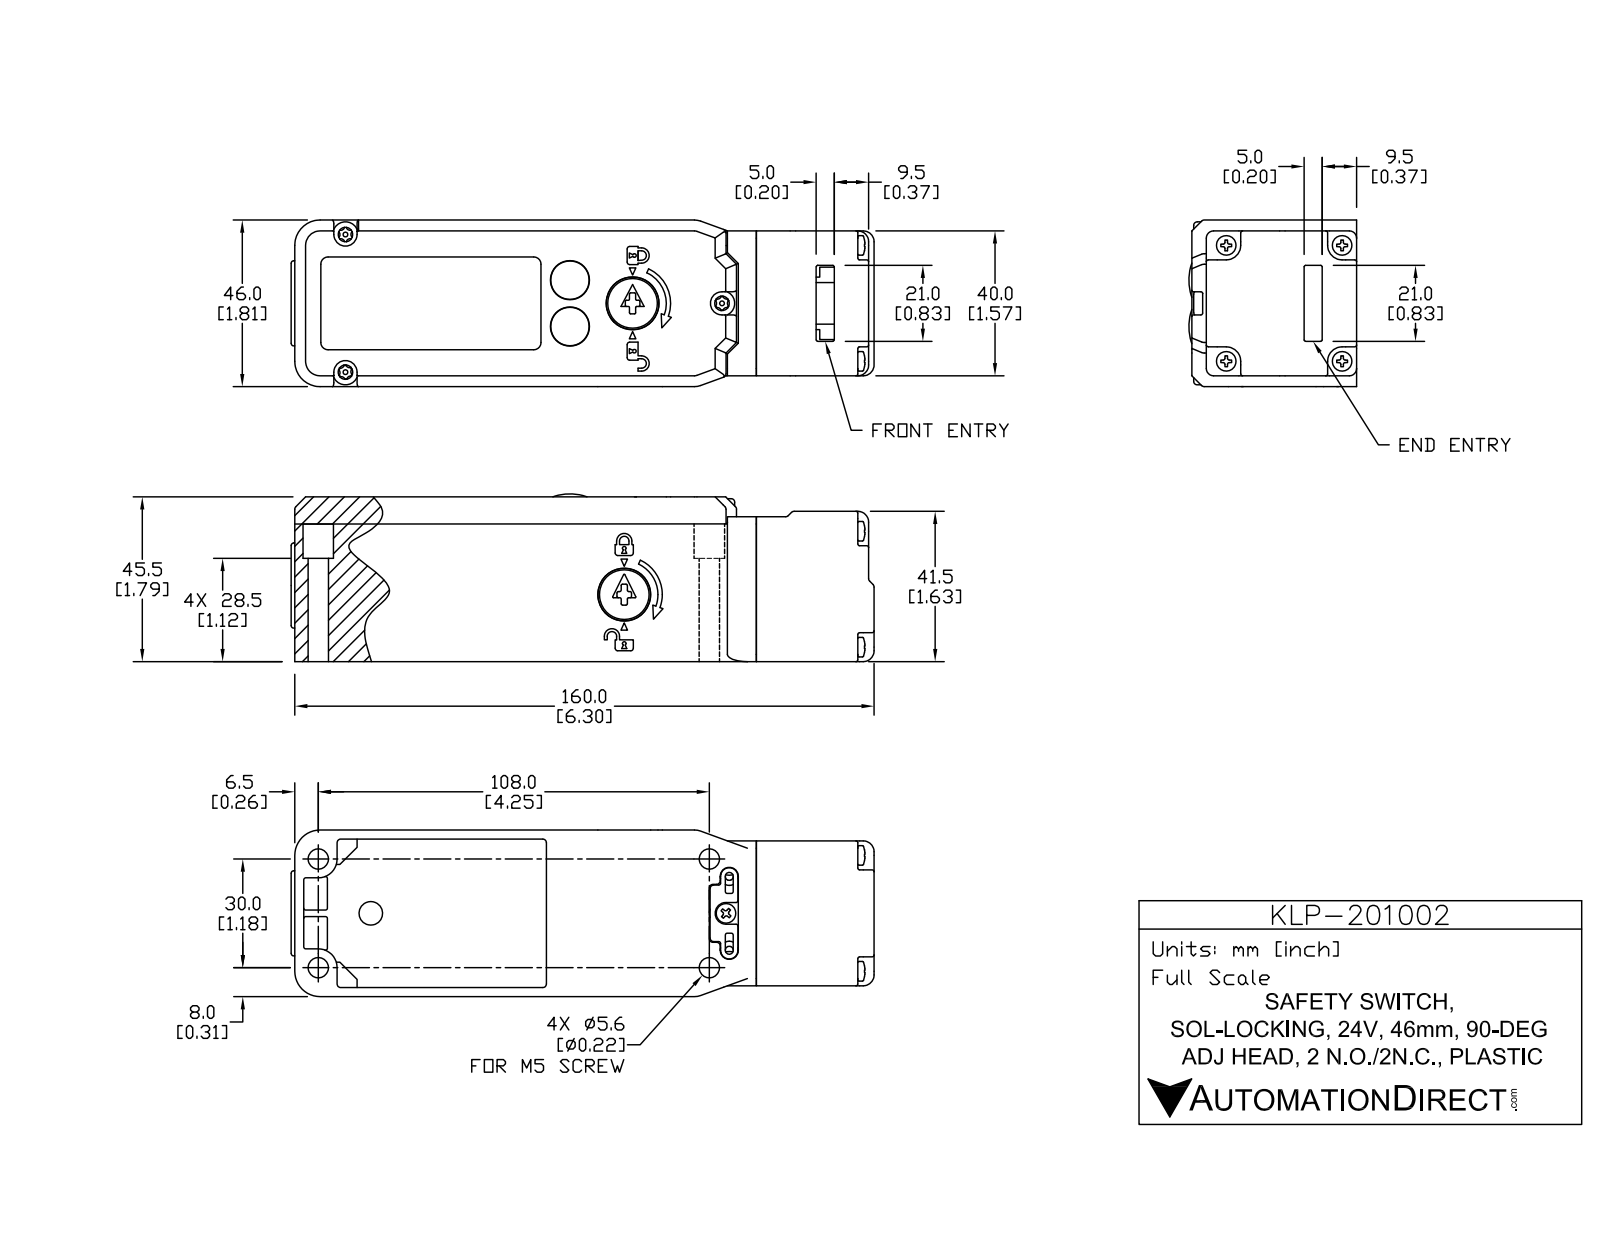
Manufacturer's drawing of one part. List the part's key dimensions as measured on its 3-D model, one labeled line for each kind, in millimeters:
Part name (STEP PRODUCT): KLP-201002
STEP written by: SolidWorks 2017 (AUTOMOTIVE_DESIGN)
Units: millimetres
Bodies: 8 solids, 476 faces (172 planar, 208 cylindrical, 96 other)
Overall size (bounding box): 161 × 46.3 × 46
Volume: 300 700 mm³ · Surface area: 51 540 mm²
Round holes (diameter × count): ⌀5.3 ×4, ⌀9.8 ×4, ⌀10.8 ×2, ⌀7 ×1
Round bosses / shafts (diameter × count): ⌀5.4 ×4, ⌀1.3 ×3, ⌀7 ×2, ⌀23.5 ×1
Partial cylindrical surfaces — rounded edges, fillets, slot ends (radius × count): R0.5 ×65, R1 ×21, R2 ×11, R3 ×4, R4 ×4, R2.5 ×3, R1.1 ×2, R5 ×2
Main face-to-face distances: 38, 46, 45.5, 7.5, 3, 43, 40, 9.5, 127.5, 127.5
Hole centre spacings: 30, 39.4, 44, 70, 72.7, 108, 112.1, 8.5
